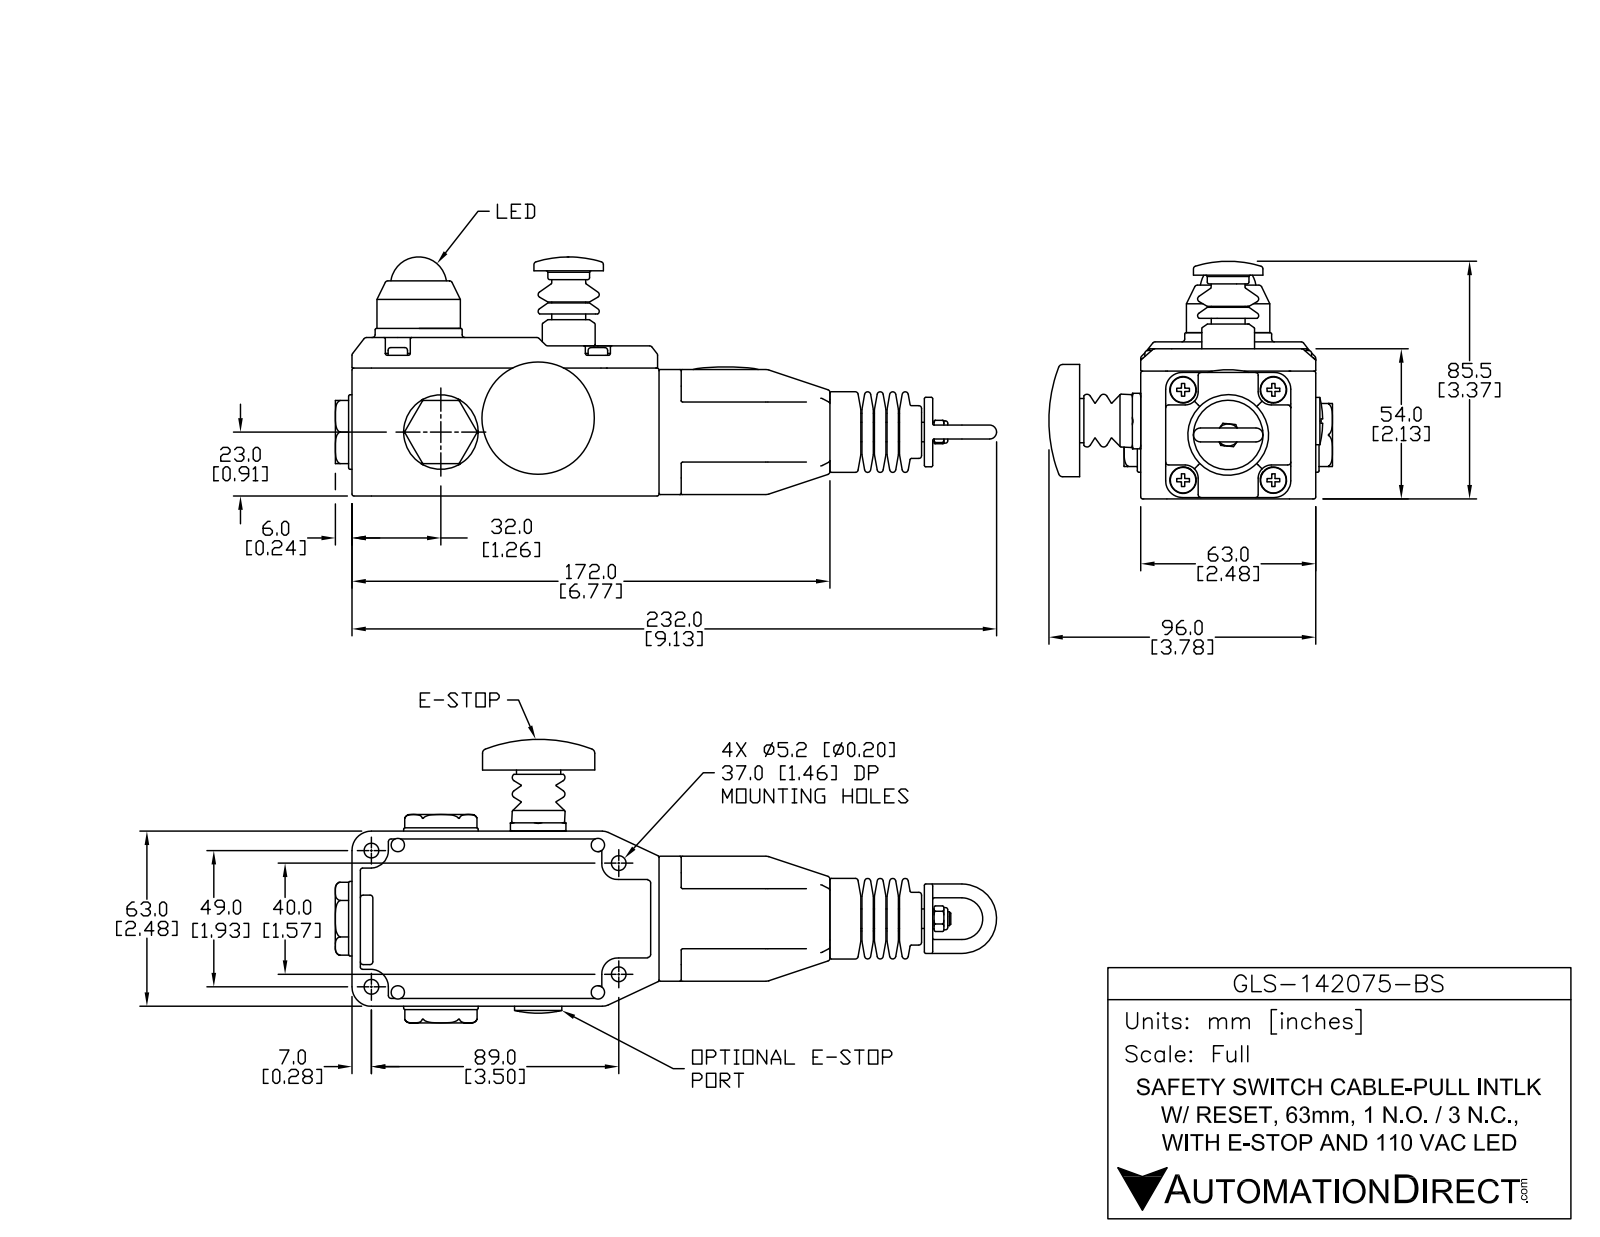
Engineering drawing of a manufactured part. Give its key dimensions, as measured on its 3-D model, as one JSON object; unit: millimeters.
{"part_name": "GLS-142075-BS", "step_written_by": "SolidWorks 2013 (AUTOMOTIVE_DESIGN)", "units": "millimeters", "bodies": {"solids": 2, "faces": 684, "planar": 222, "cylindrical": 225, "other": 237}, "overall_size": [238, 102.3, 86], "volume_mm3": 516211, "surface_area_mm2": 66955, "round_holes": [[4.75, 4], [9.5, 4], [5, 2], [5.2, 2], [15, 1], [34, 1]], "round_bosses_or_shafts": [[9.2, 4], [6, 4], [26.8, 2], [25, 2], [12, 2], [5, 2], [40, 1], [31.3, 1]], "partial_cylinders_radius": [[0.5, 52], [0.75, 20], [1.1, 6], [4, 4], [4.5, 4], [4.8, 4], [16, 4], [5.8, 2]], "face_to_face_distances": [63, 54, 56.68, 9, 3, 11.7, 33.3, 53.68, 45, 4.5], "hole_center_spacings": [9.6, 9.62, 26.78, 29.22, 32.4, 32.6, 45.96, 46.61]}
